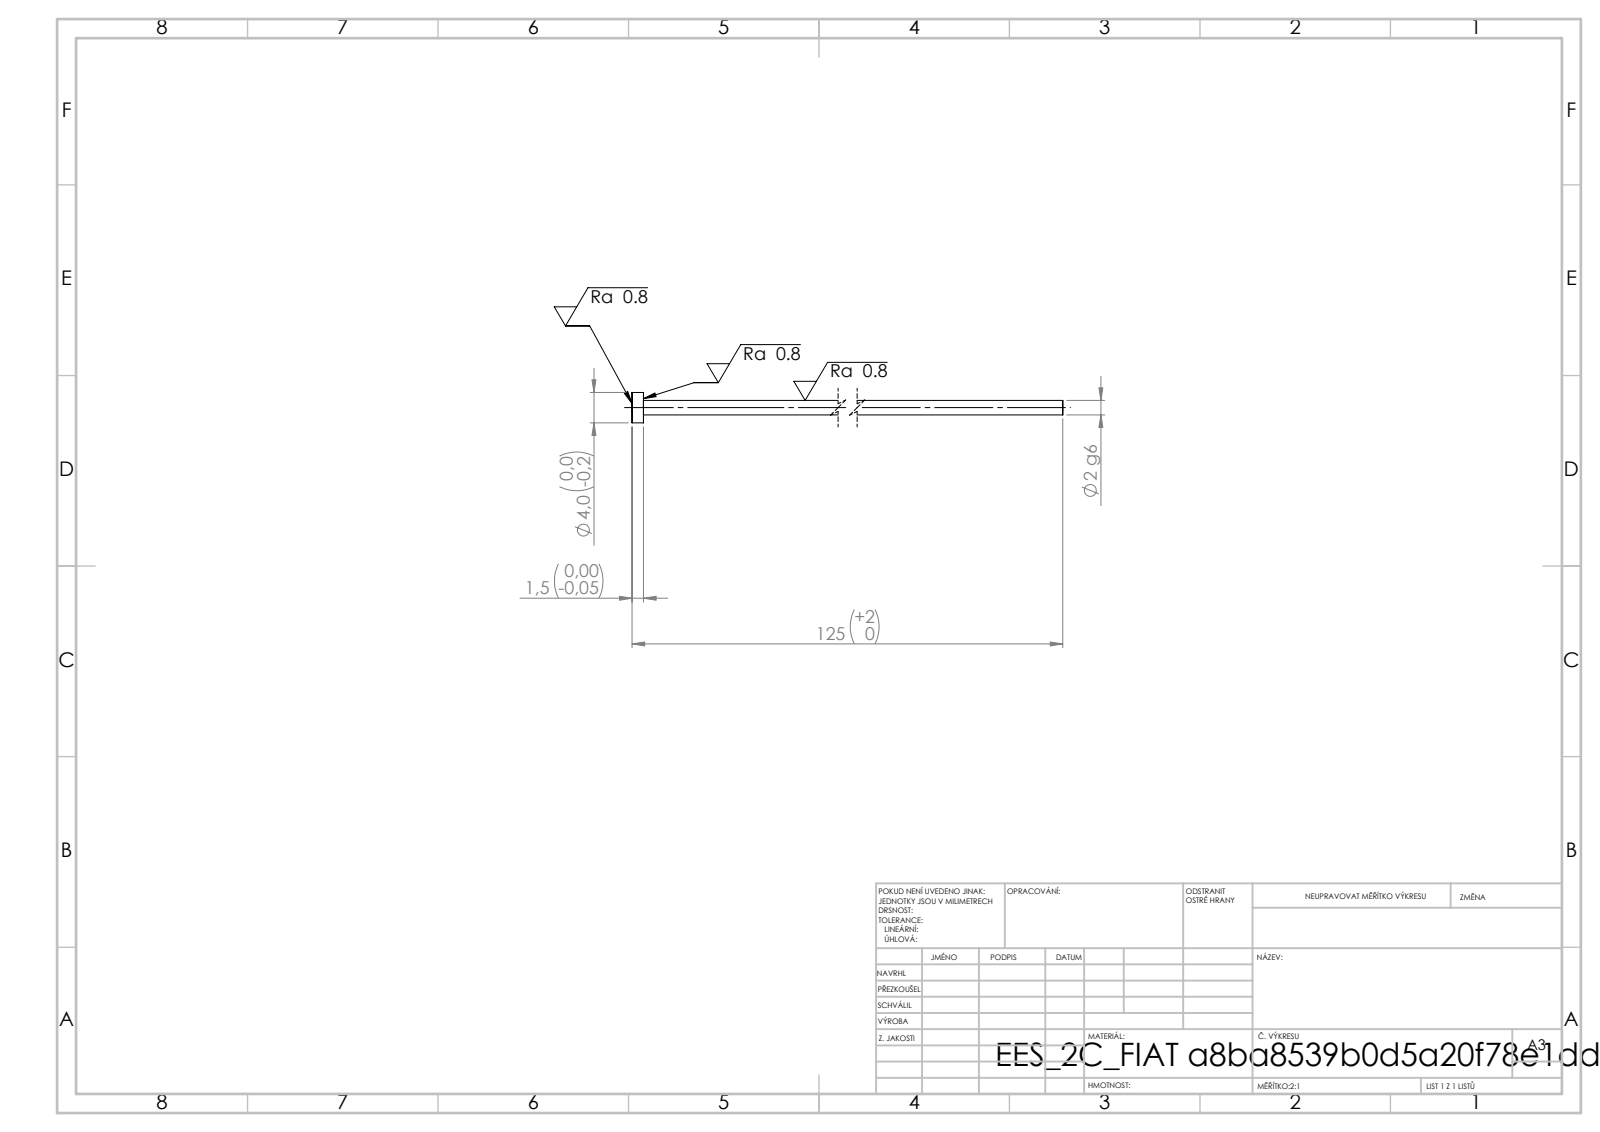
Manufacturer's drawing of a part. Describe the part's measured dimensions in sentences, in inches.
Its 3-D file was written by "SolidWorks 2019 (CONFIG_CONTROL_DESIGN)". It is 1 solid with 7 faces: 3 planar, 4 cylindrical and 0 other. Overall it measures 4.921 by 0.157 by 0.157 inches. Its volume is 0.023 cubic inches and its surface area 1.21 square inches. Round bosses or shafts: 1 of diameter 0.157, 1 of diameter 0.075. The main face-to-face distances are 0.059, 4.921, 4.862.
